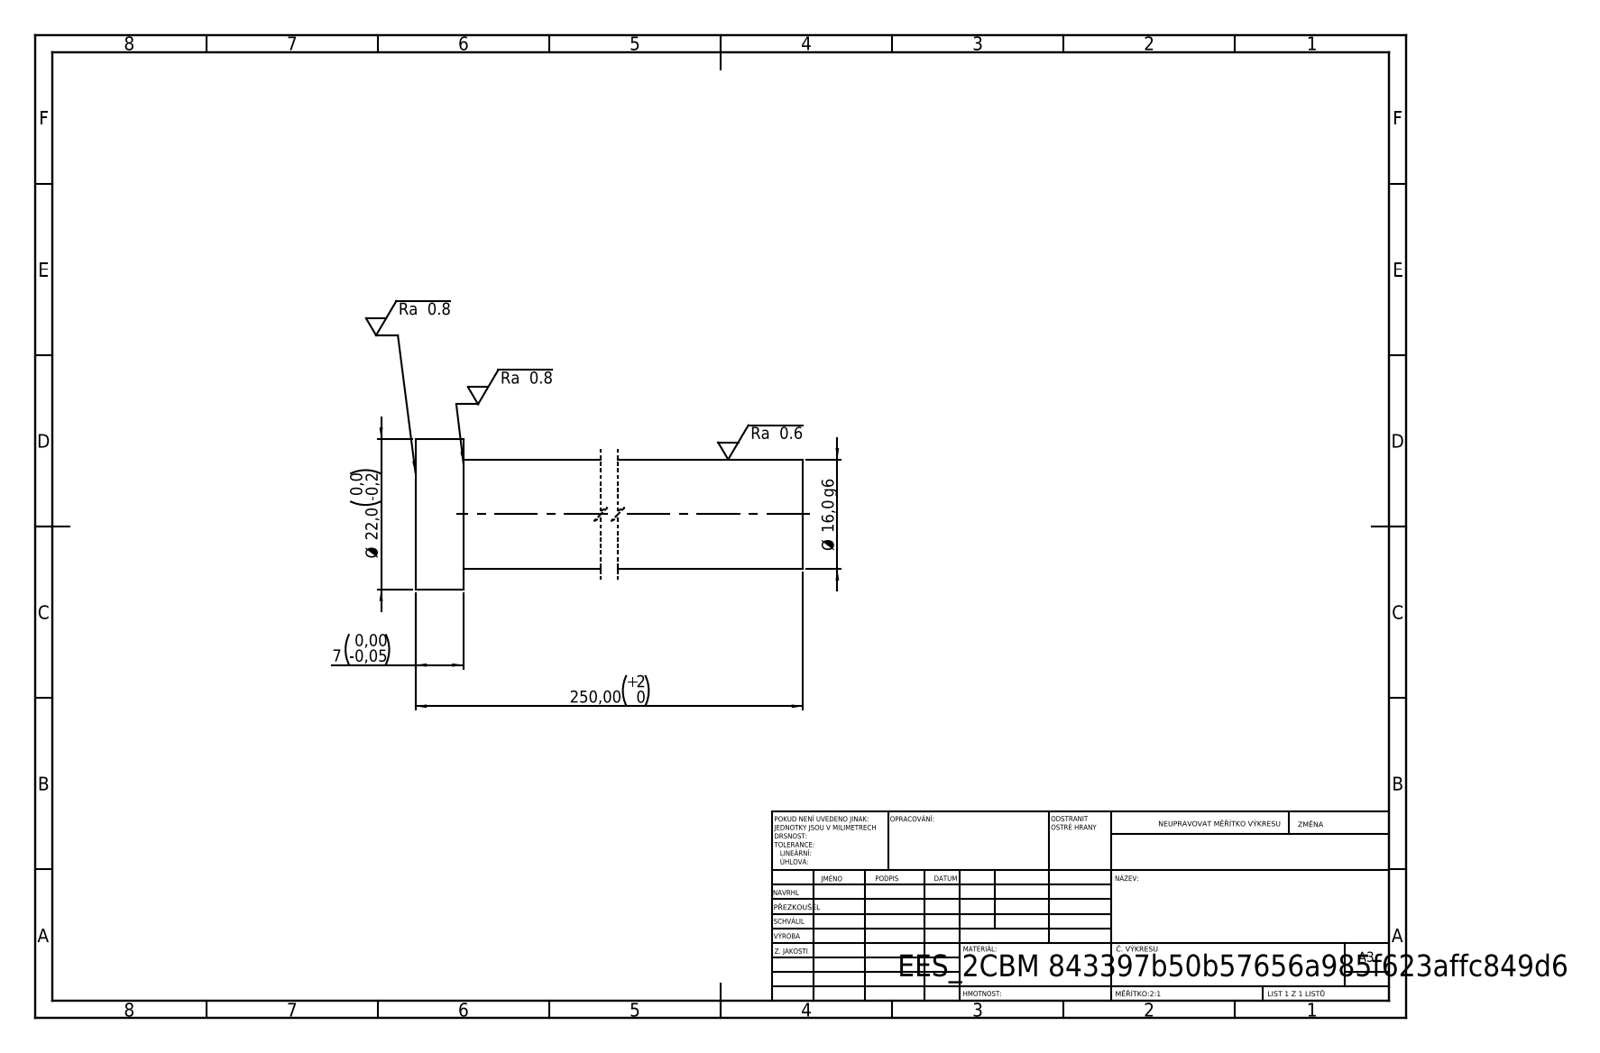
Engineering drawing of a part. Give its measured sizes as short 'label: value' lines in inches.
written by: SolidWorks 2019 (CONFIG_CONTROL_DESIGN)
unit: in
bodies: 1 solid, 7 faces (3 planar, 4 cylindrical, 0 other)
size: 9.843 × 0.866 × 0.866
volume: 3.144 in³; area: 20.86 in²
bosses: 1× ⌀0.866, 1× ⌀0.63
face distances: 9.843, 0.276, 9.567
